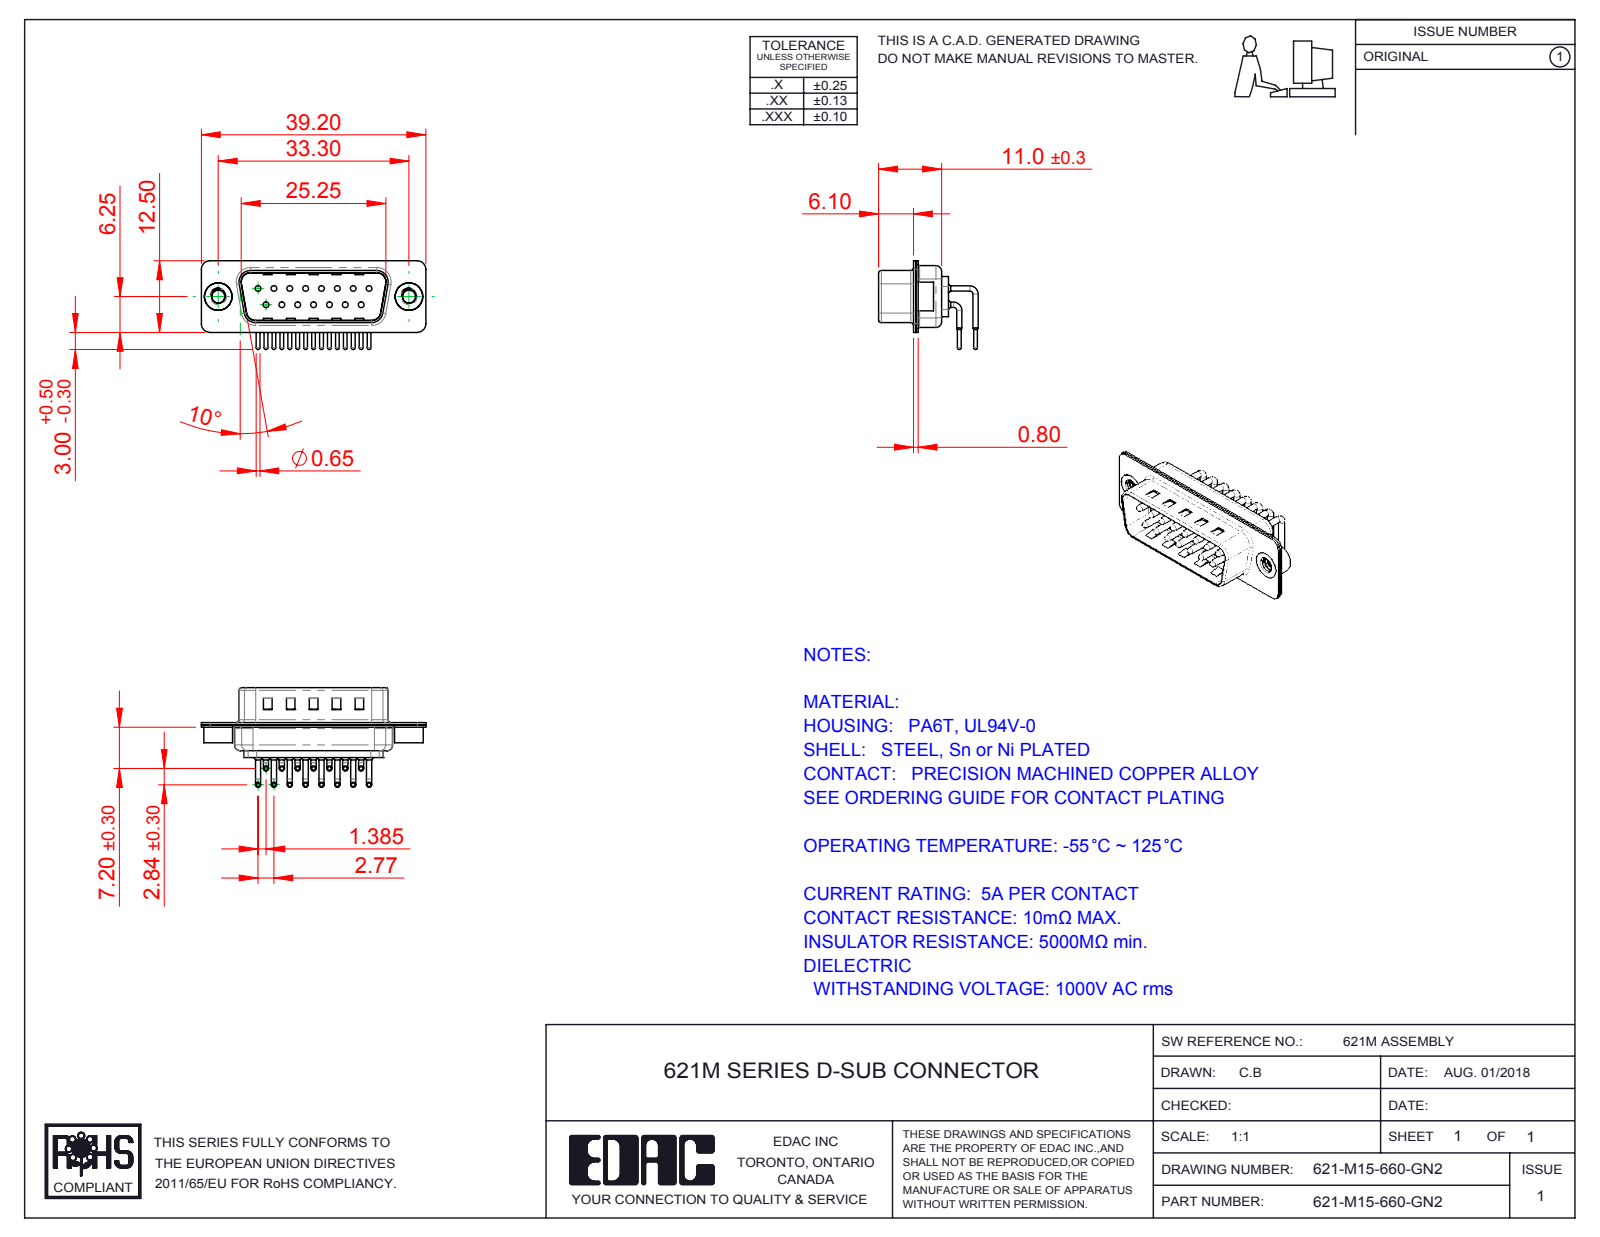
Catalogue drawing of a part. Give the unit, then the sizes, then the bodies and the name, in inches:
Units: inches
Overall size (bounding box): 1.543 × 0.685 × 0.61
Round holes (diameter × count): ⌀0.039 ×15, ⌀0.067 ×15, ⌀0.079 ×15, ⌀0.089 ×2, ⌀0.157 ×2, ⌀0.189 ×2
Round bosses / shafts (diameter × count): ⌀0.035 ×30, ⌀0.059 ×15, ⌀0.026 ×15, ⌀0.197 ×2, ⌀0.193 ×2
Partial cylindrical surfaces — rounded edges, fillets, slot ends (radius × count): R0.059 ×16, R0.04 ×15, R0.079 ×12, R0.02 ×8, R0.063 ×8, R0.01 ×4, R0.024 ×4, R0.026 ×4
Main face-to-face distances: 0.016, 0.033, 0.376, 0.343, 0.049, 0.409, 0.031, 0.059, 0.014, 0.075
Hole centre spacings: 0.124, 0.109, 0.218, 0.327, 0.436, 0.198, 0.198, 0.294
Volume: 0.118 in³ · Surface area: 8.156 in²
Bodies: 20 solids, 1990 faces (1099 planar, 673 cylindrical, 218 other)
Part name (STEP PRODUCT): 621M Shell Front_15 Contacts; 621M Housing_15 Contacts; 621M Contact Row 2; 621-M15-660-GN2 (+3 more)
STEP written by: SolidWorks 2016 (CONFIG_CONTROL_DESIGN)
